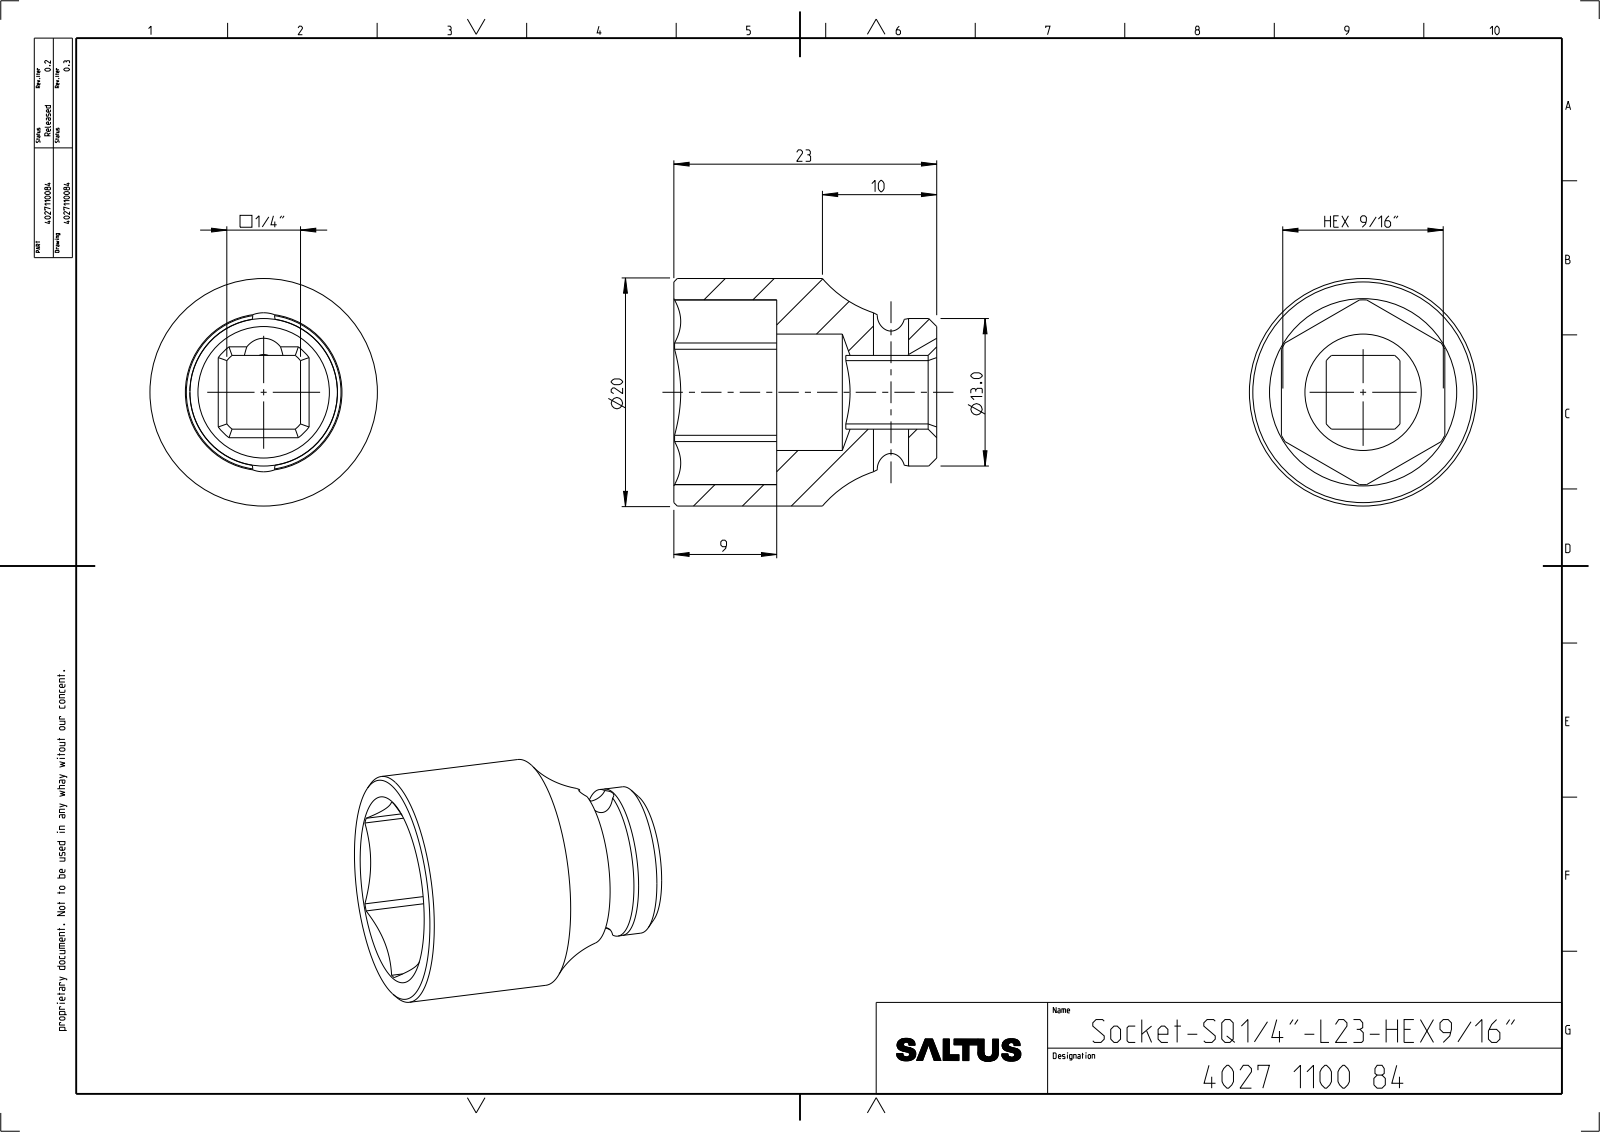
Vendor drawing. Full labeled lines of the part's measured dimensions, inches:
Part name (STEP PRODUCT): 4027110084
STEP written by: CREO PARAMETRIC BY PTC INC, 2022414 (CONFIG_CONTROL_DESIGN)
Units: inches
Bodies: 1 solid, 59 faces (20 planar, 21 cylindrical, 18 other)
Overall size (bounding box): 0.906 × 0.783 × 0.783
Volume: 0.194 in³ · Surface area: 3.88 in²
Round holes (diameter × count): ⌀0.121 ×1, ⌀0.401 ×1
Round bosses / shafts (diameter × count): ⌀0.783 ×1, ⌀0.508 ×1
Partial cylindrical surfaces — rounded edges, fillets, slot ends (radius × count): R0.079 ×1, R0.167 ×1, R0.318 ×1
Main face-to-face distances: 0.563, 0.354, 0.154, 0.409, 0.254, 0.551, 0.906, 0.205, 0.346, 0.701
